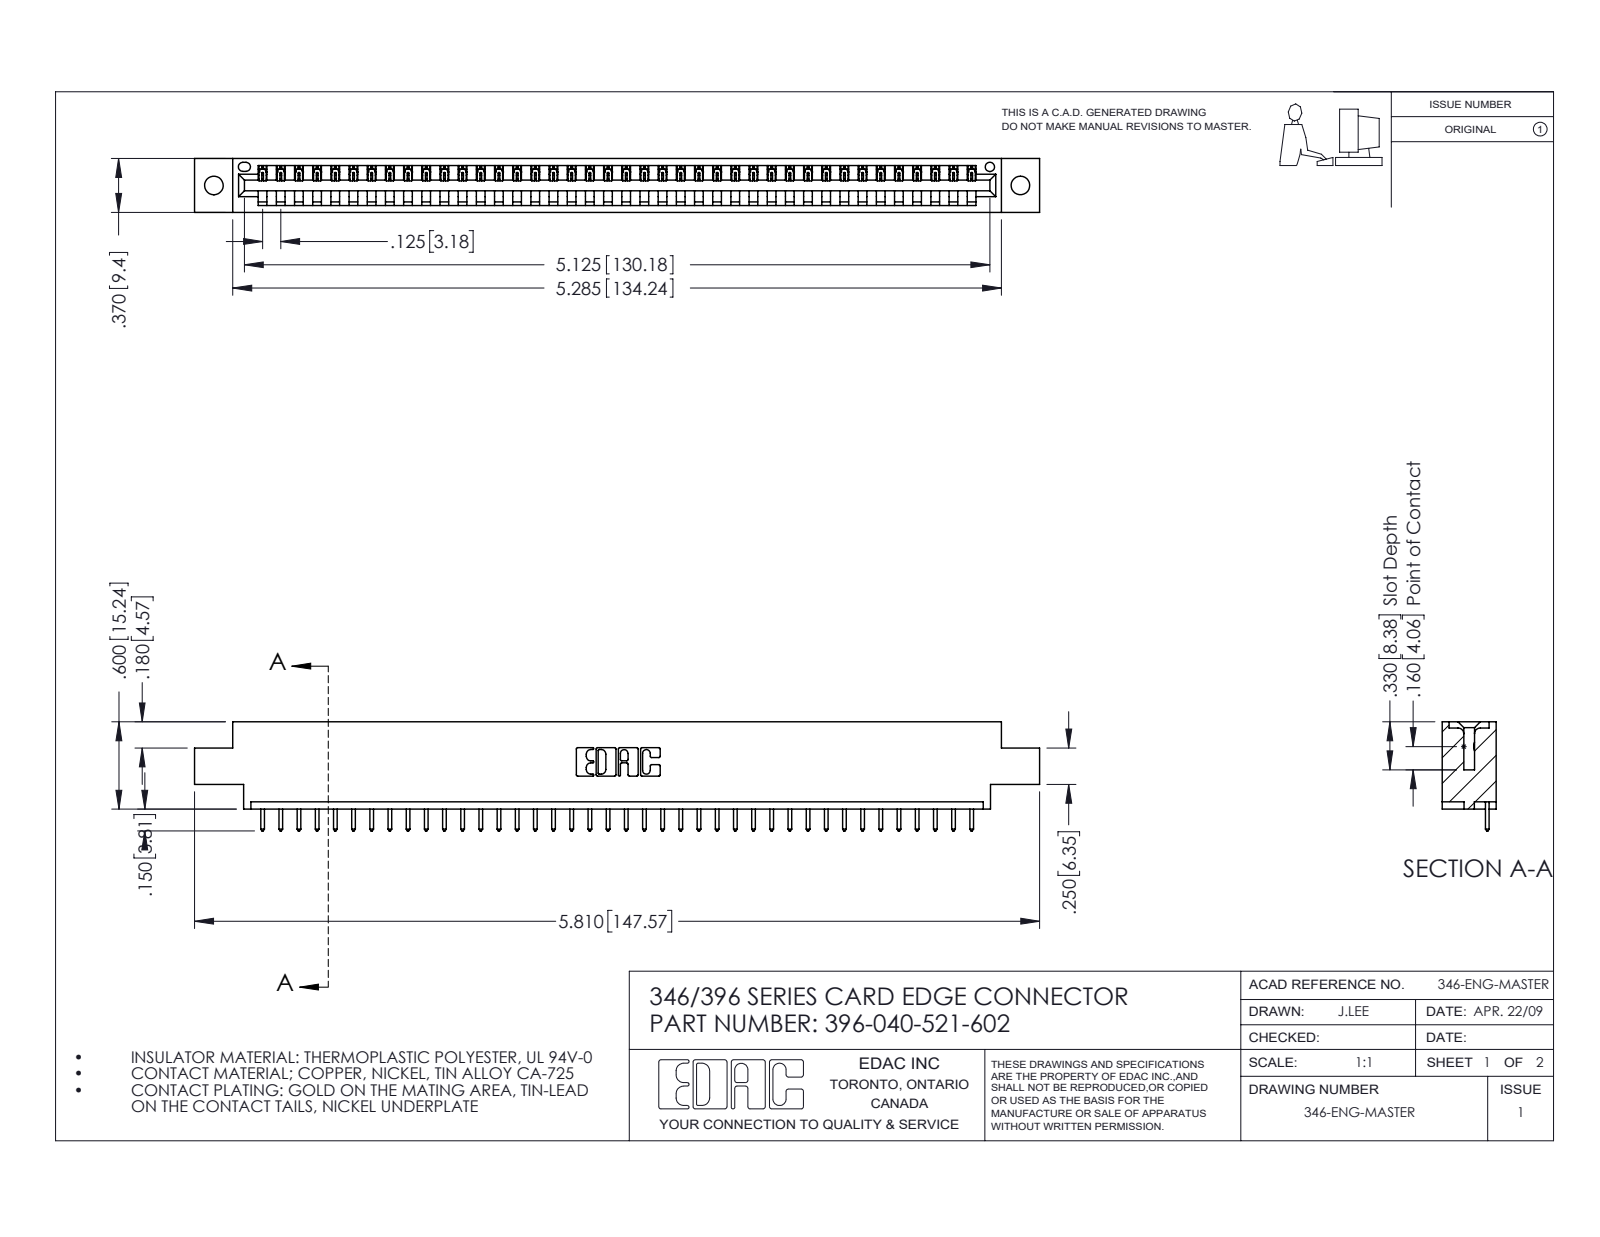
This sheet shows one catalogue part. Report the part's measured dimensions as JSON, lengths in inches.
{"part_name": "345-292-001_345-293-121; 396-040-521-602; 346 Part_0.170 Offset - 0.128 Dia", "step_written_by": "SolidWorks 2016 (CONFIG_CONTROL_DESIGN)", "units": "inches", "bodies": {"solids": 41, "faces": 2446, "planar": 1680, "cylindrical": 766, "other": 0}, "overall_size": [5.81, 0.75, 0.37], "volume_in3": 0.843, "surface_area_in2": 25.84, "round_holes": [[0.128, 2], [0.064, 1]], "partial_cylinders_radius": [[0.006, 80], [0.01, 80], [0.01, 22], [0.007, 6], [0.031, 6], [0.026, 3], [0.031, 2], [0.04, 2]], "face_to_face_distances": [0.048, 0.322, 0.37, 0.25, 0.072, 0.298, 0.025, 0.148, 0.222, 0.1], "hole_center_spacings": [0.246, 5.336, 5.545]}
